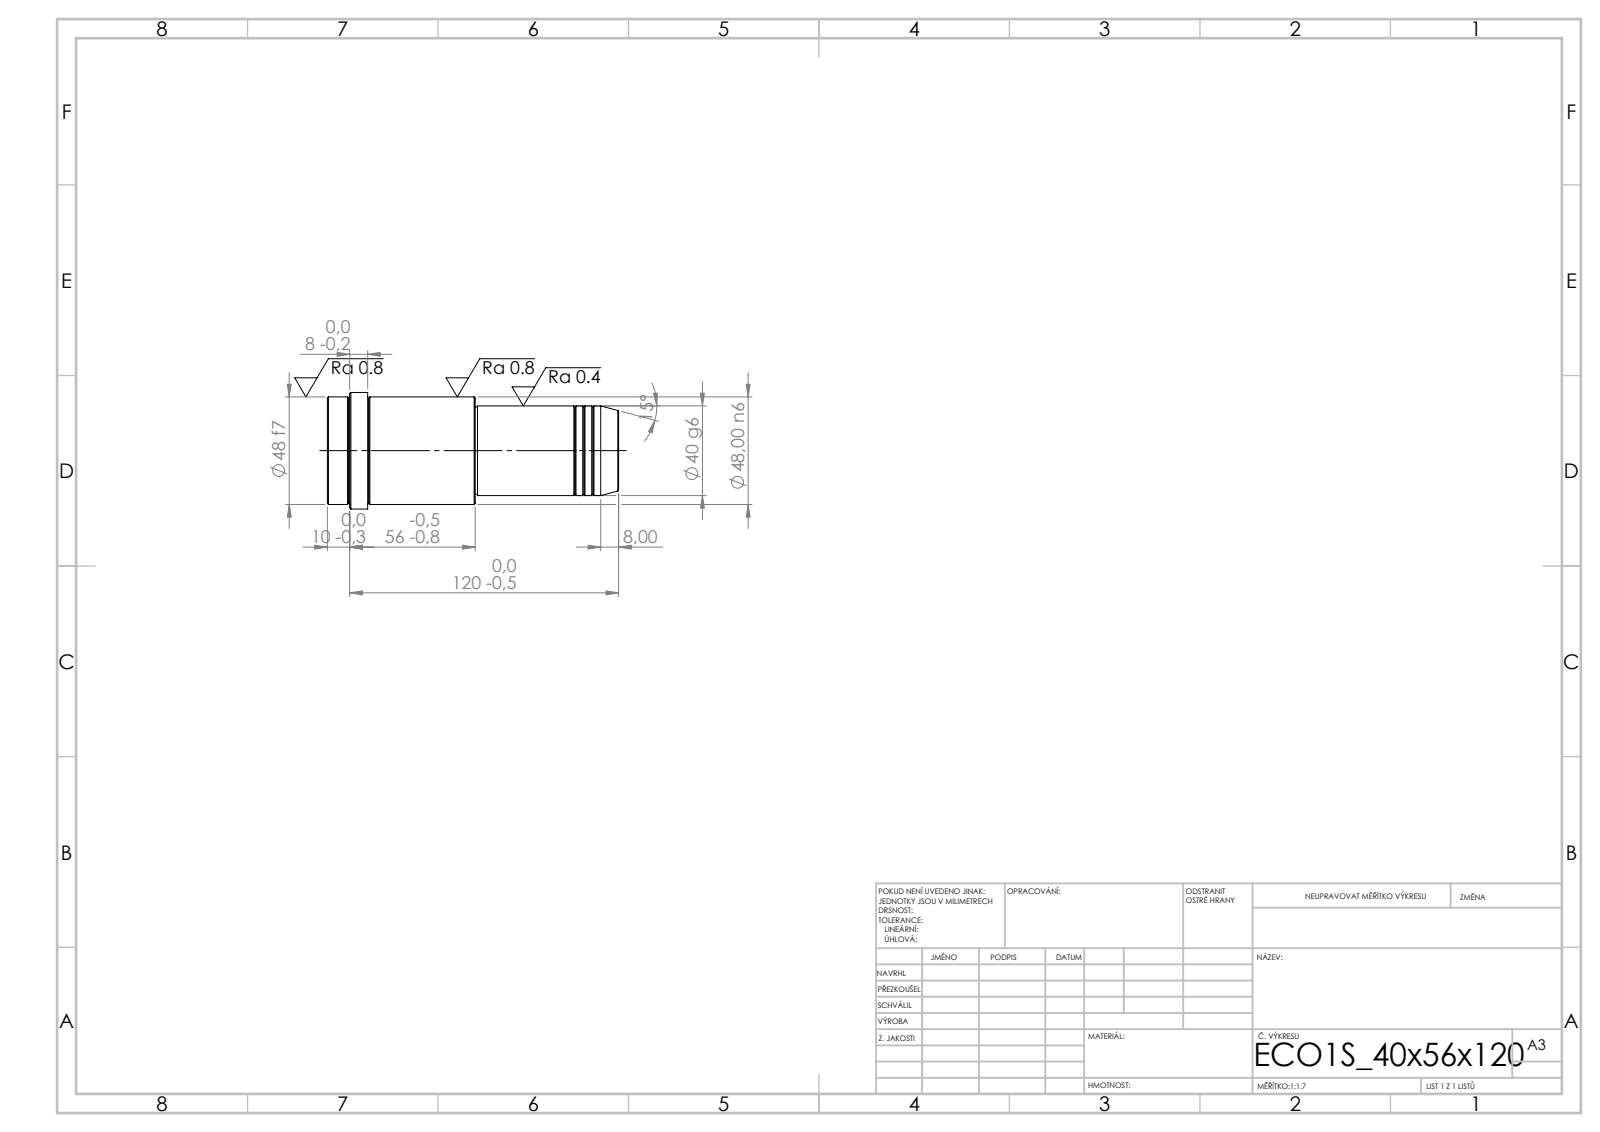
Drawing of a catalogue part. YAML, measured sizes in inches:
step_written_by: "SolidWorks 2019 (CONFIG_CONTROL_DESIGN)"
units: inches
bodies: {solids: 1, faces: 52, planar: 6, cylindrical: 16, other: 30}
overall_size: [5.118, 2.047, 2.047]
volume: 12.26
surface_area: 34.74
round_bosses_or_shafts:
  - {diameter: 2.047, count: 1}
  - {diameter: 1.89, count: 1}
  - {diameter: 1.575, count: 1}
  - {diameter: 1.535, count: 1}
face_to_face_distances: [5.118, 2.52, 2.598, 4.409, 1.89, 0.709, 4.724, 2.205, 0.315, 0.394]
